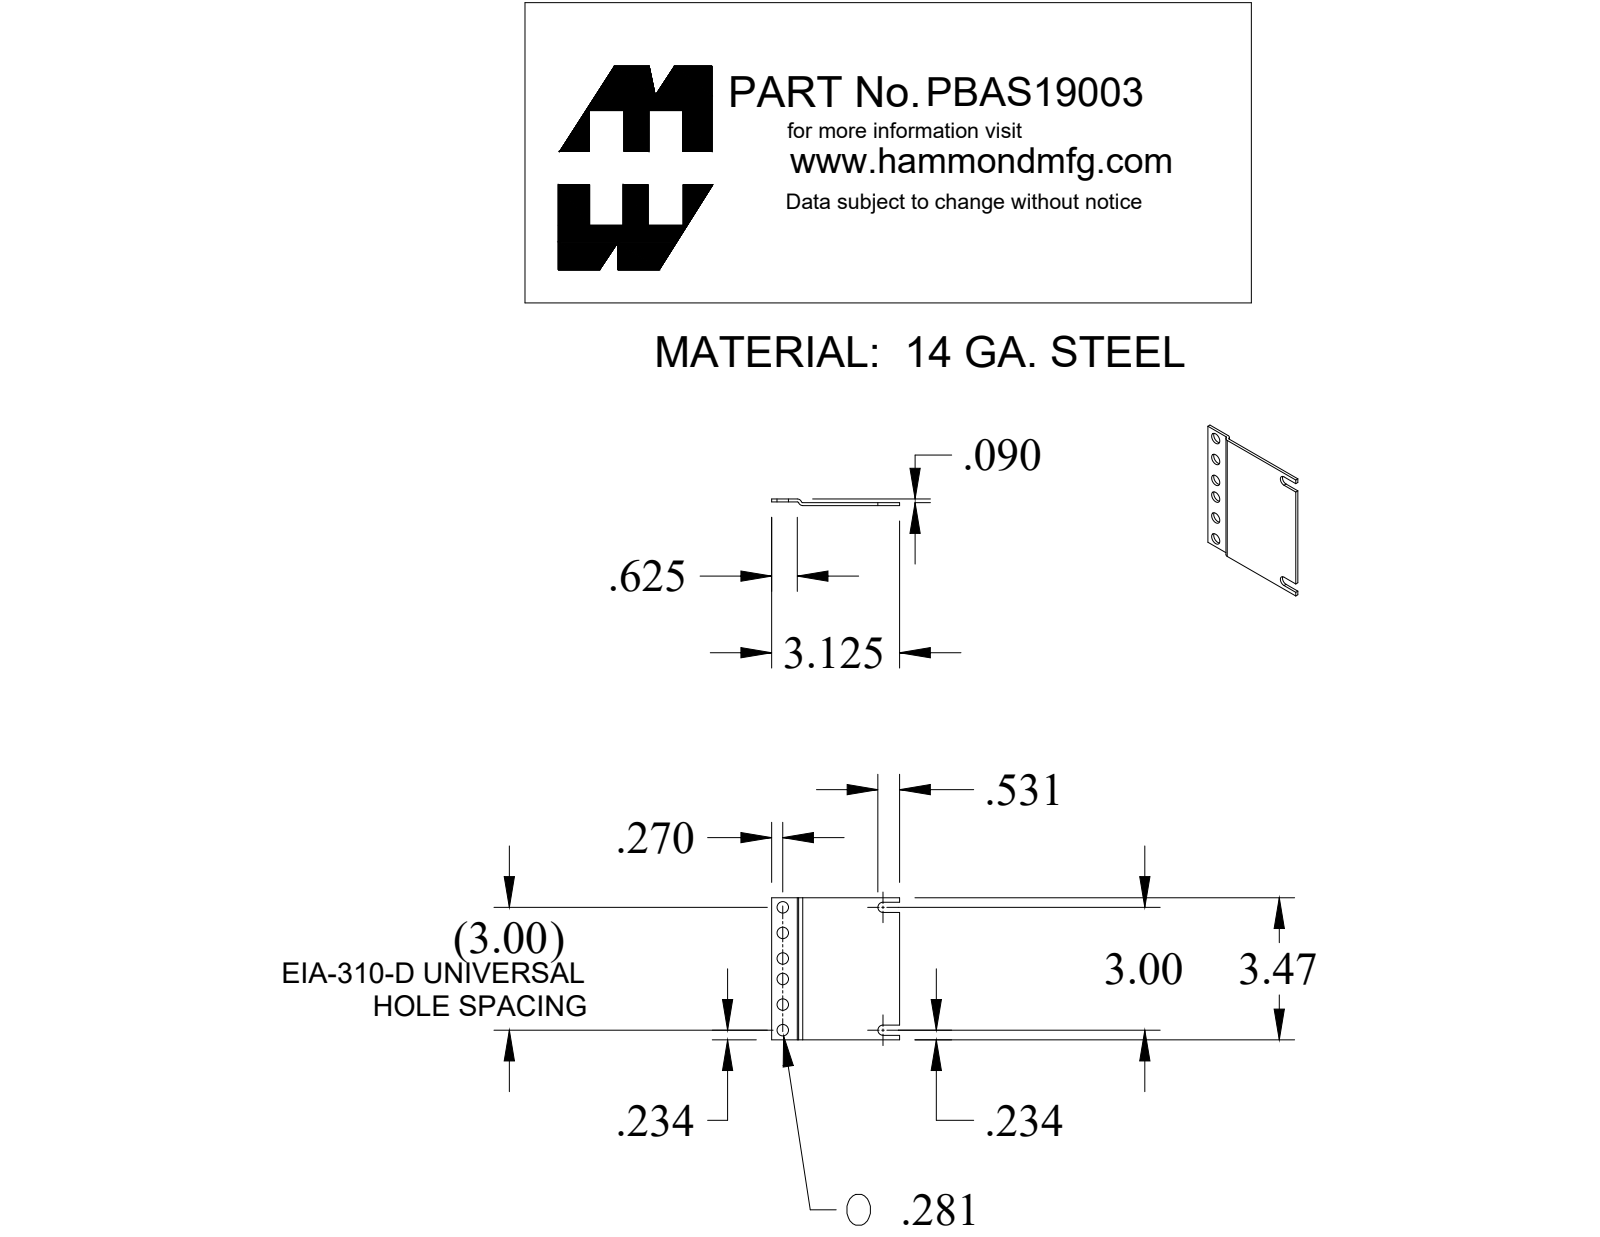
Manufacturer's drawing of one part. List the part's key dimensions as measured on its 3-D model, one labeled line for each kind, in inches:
Part name (STEP PRODUCT): PBAS19003BK2
STEP written by: SolidWorks 2019 (CONFIG_CONTROL_DESIGN)
Units: inches
Bodies: 1 solid, 26 faces (14 planar, 12 cylindrical, 0 other)
Overall size (bounding box): 3.468 × 3.125 × 0.162
Volume: 0.745 in³ · Surface area: 22.16 in²
Round holes (diameter × count): ⌀0.281 ×6
Partial cylindrical surfaces — rounded edges, fillets, slot ends (radius × count): R0.036 ×2, R0.108 ×2, R0.125 ×2
Main face-to-face distances: 0.072, 0.09, 0.162, 0.018, 0.09, 0.072, 3.468, 3.125, 0.109, 3.359
Hole centre spacings: 0.625, 0.625, 1.125, 1.25, 1.75, 2.375, 0.5, 1.75
